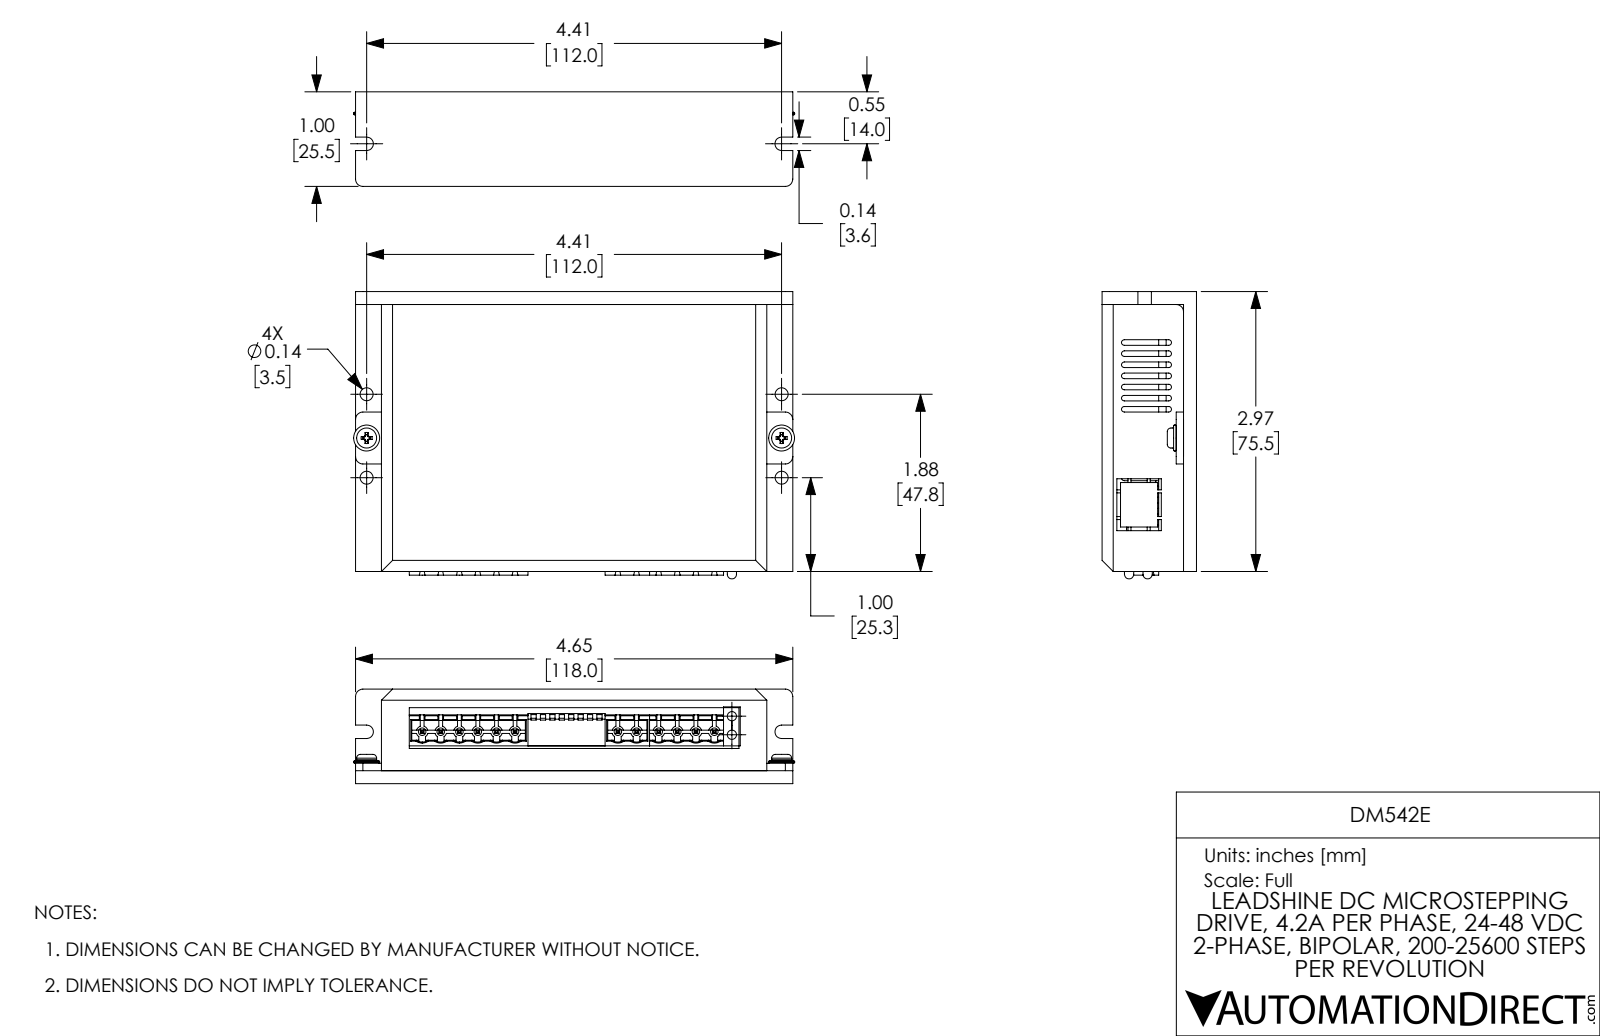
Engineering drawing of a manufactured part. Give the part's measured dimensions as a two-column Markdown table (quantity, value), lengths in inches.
| quantity | value |
| --- | --- |
| part name | DM542E_3D |
| STEP written by | SolidWorks 2017 (AUTOMOTIVE_DESIGN) |
| units | inches |
| bodies | 10 solids, 1394 faces (1045 planar, 287 cylindrical, 62 other) |
| overall size | 4.685 × 3.051 × 1.004 |
| volume | 4.784 in³ |
| surface area | 107.6 in² |
| round holes (diameter × count) | 0.08 × 12, 0.03 × 8, 0.138 × 6 |
| round bosses / shafts (diameter × count) | 0.276 × 2, 0.213 × 2, 0.118 × 2, 0.098 × 2, 0.093 × 2, 0.016 × 2, 0.593 × 1 |
| partial cylindrical surfaces (radius × count) | 0.03 × 28, 0.061 × 12, 0.11 × 12, 0.063 × 8, 0.079 × 7, 0.062 × 4, 0.071 × 2, 0.273 × 1 |
| main face-to-face distances | 0.079, 0.602, 0.138, 0.402, 0.264, 1.004, 0.866, 0.185, 0.323, 0.681 |
| hole center spacings | 0.038, 0.076, 0.113, 0.198, 0.591, 1.882, 4.409, 0.038 |
